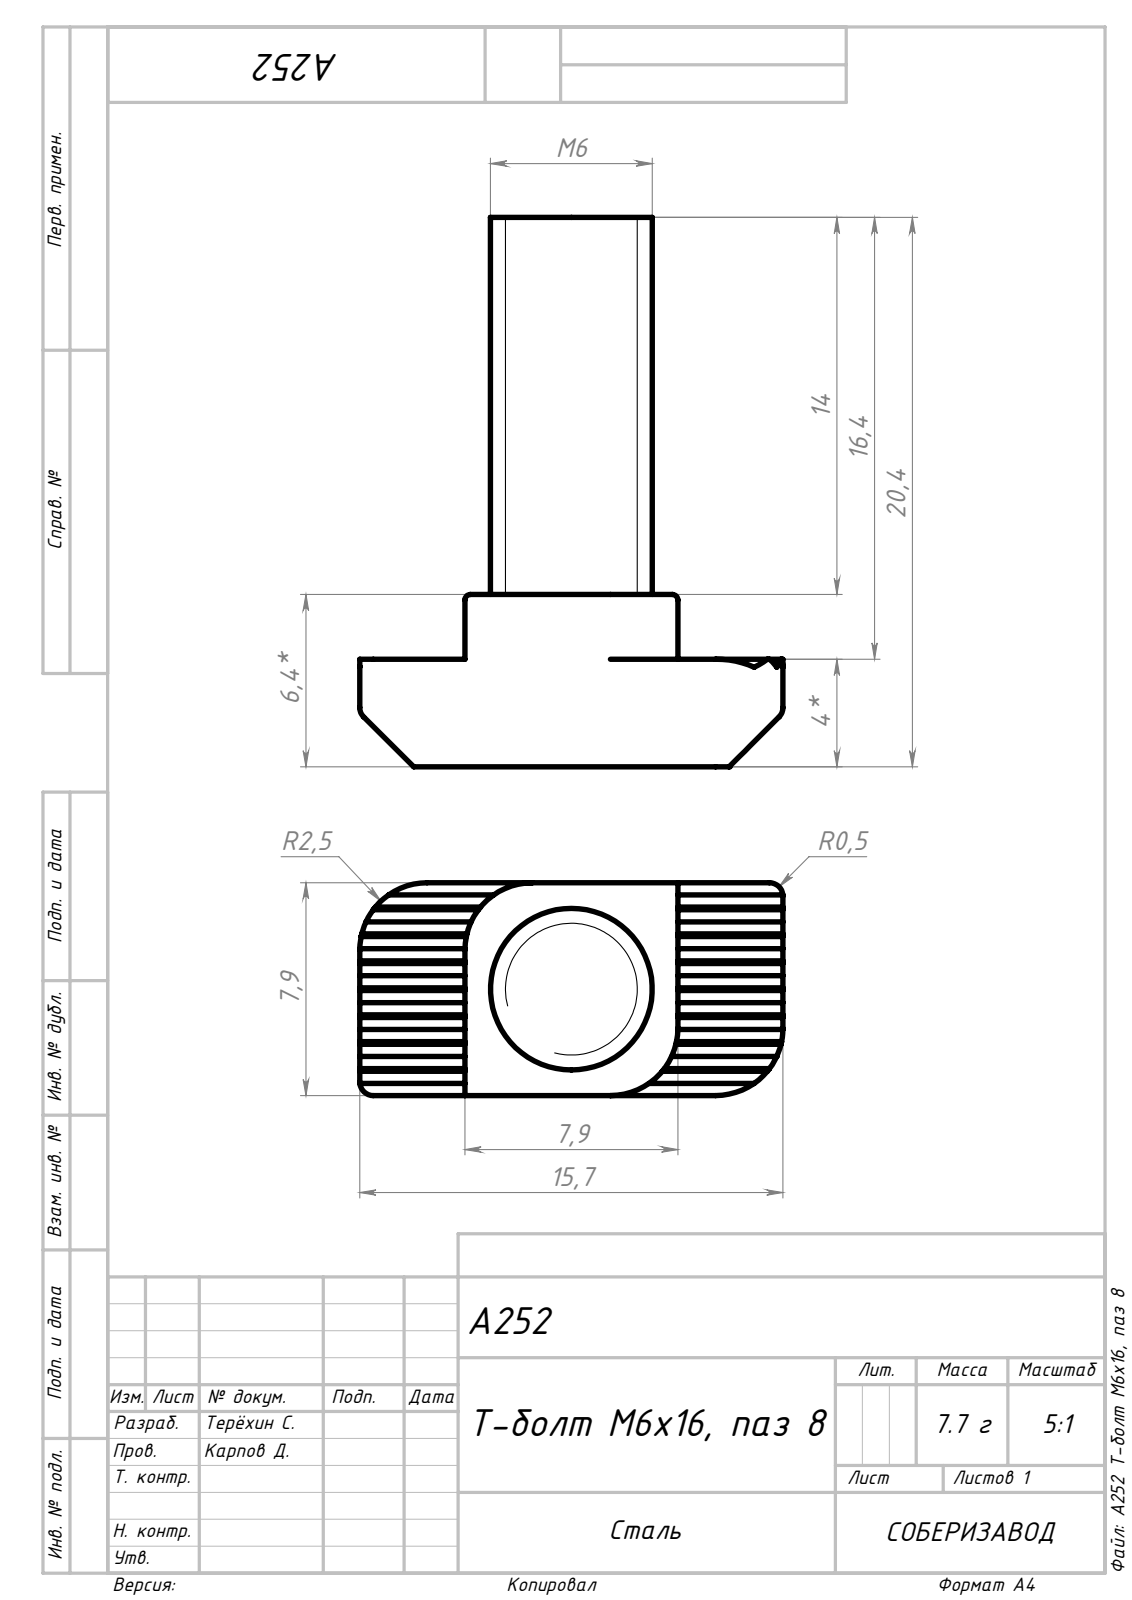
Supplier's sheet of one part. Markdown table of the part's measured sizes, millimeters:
| quantity | value |
| --- | --- |
| part name | A252 Т-болт М6х16, паз 8 |
| STEP written by | SolidWorks 2021 (AUTOMOTIVE_DESIGN) |
| units | millimeters |
| bodies | 1 solid, 83 faces (57 planar, 18 cylindrical, 8 other) |
| overall size | 20.4 × 15.7 × 7.9 |
| volume | 986 mm³ |
| surface area | 736 mm² |
| round bosses / shafts (diameter × count) | 6 × 1 |
| partial cylindrical surfaces (radius × count) | 0.5 × 8, 0.2 × 4, 2.5 × 4 |
| main face-to-face distances | 7.9, 1.11, 0.55, 2.22, 20.4, 6.4, 14, 0.56, 1.66, 1.67 |
